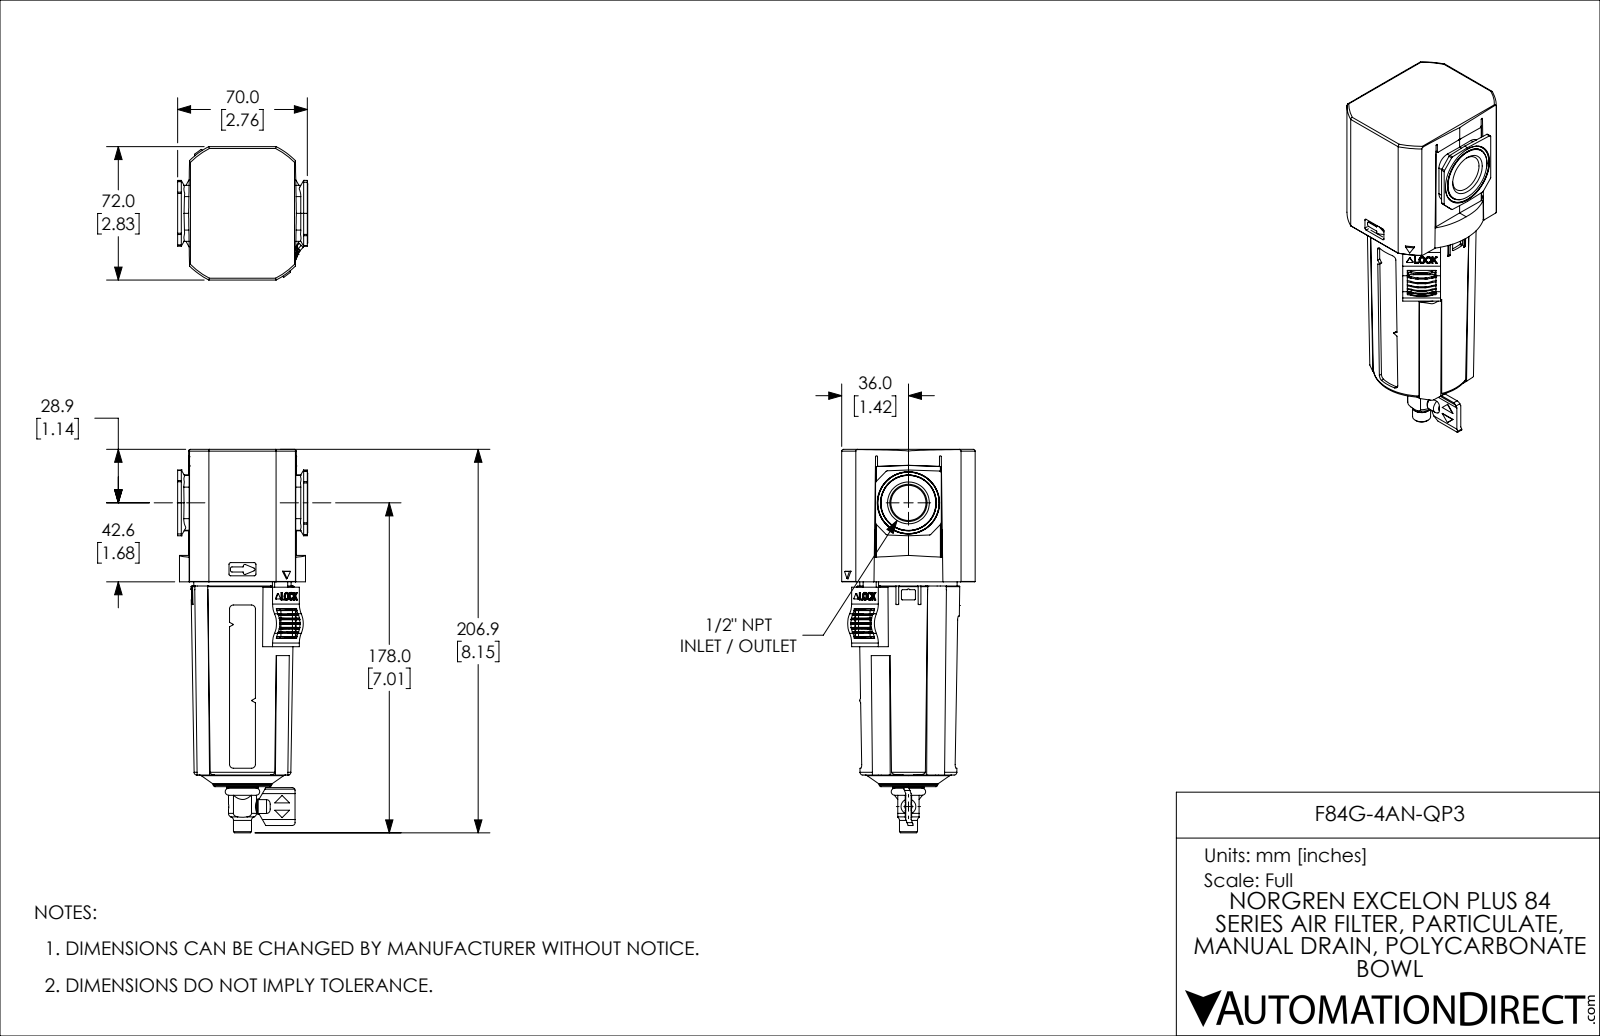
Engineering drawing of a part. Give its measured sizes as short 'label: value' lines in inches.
name: F84G-4AN-QP3
written by: SolidWorks 2021 (CONFIG_CONTROL_DESIGN)
unit: in
bodies: 5 solids, 1065 faces (481 planar, 382 cylindrical, 202 other)
size: 8.146 × 2.835 × 2.766
volume: 27.81 in³; area: 150 in²
holes: 2× ⌀0.163, 1× ⌀0.123, 1× ⌀0.126, 1× ⌀0.236, 1× ⌀0.25, 1× ⌀0.374, 1× ⌀0.969, 1× ⌀2.461
bosses: 3× ⌀0.315, 2× ⌀0.276, 1× ⌀0.906, 1× ⌀0.626, 1× ⌀0.399, 1× ⌀0.383, 1× ⌀0.22
rounds: 40× R0.02, 33× R0.039, 24× R0.01, 16× R0.028, 10× R0.008, 8× R0.038, 8× R0.045, 8× R0.06
face distances: 0.059, 2.352, 2.411, 2.835, 0.035, 2.317, 2.376, 2.756, 0.404, 0.439
hole spacings: 0.594, 1.189
